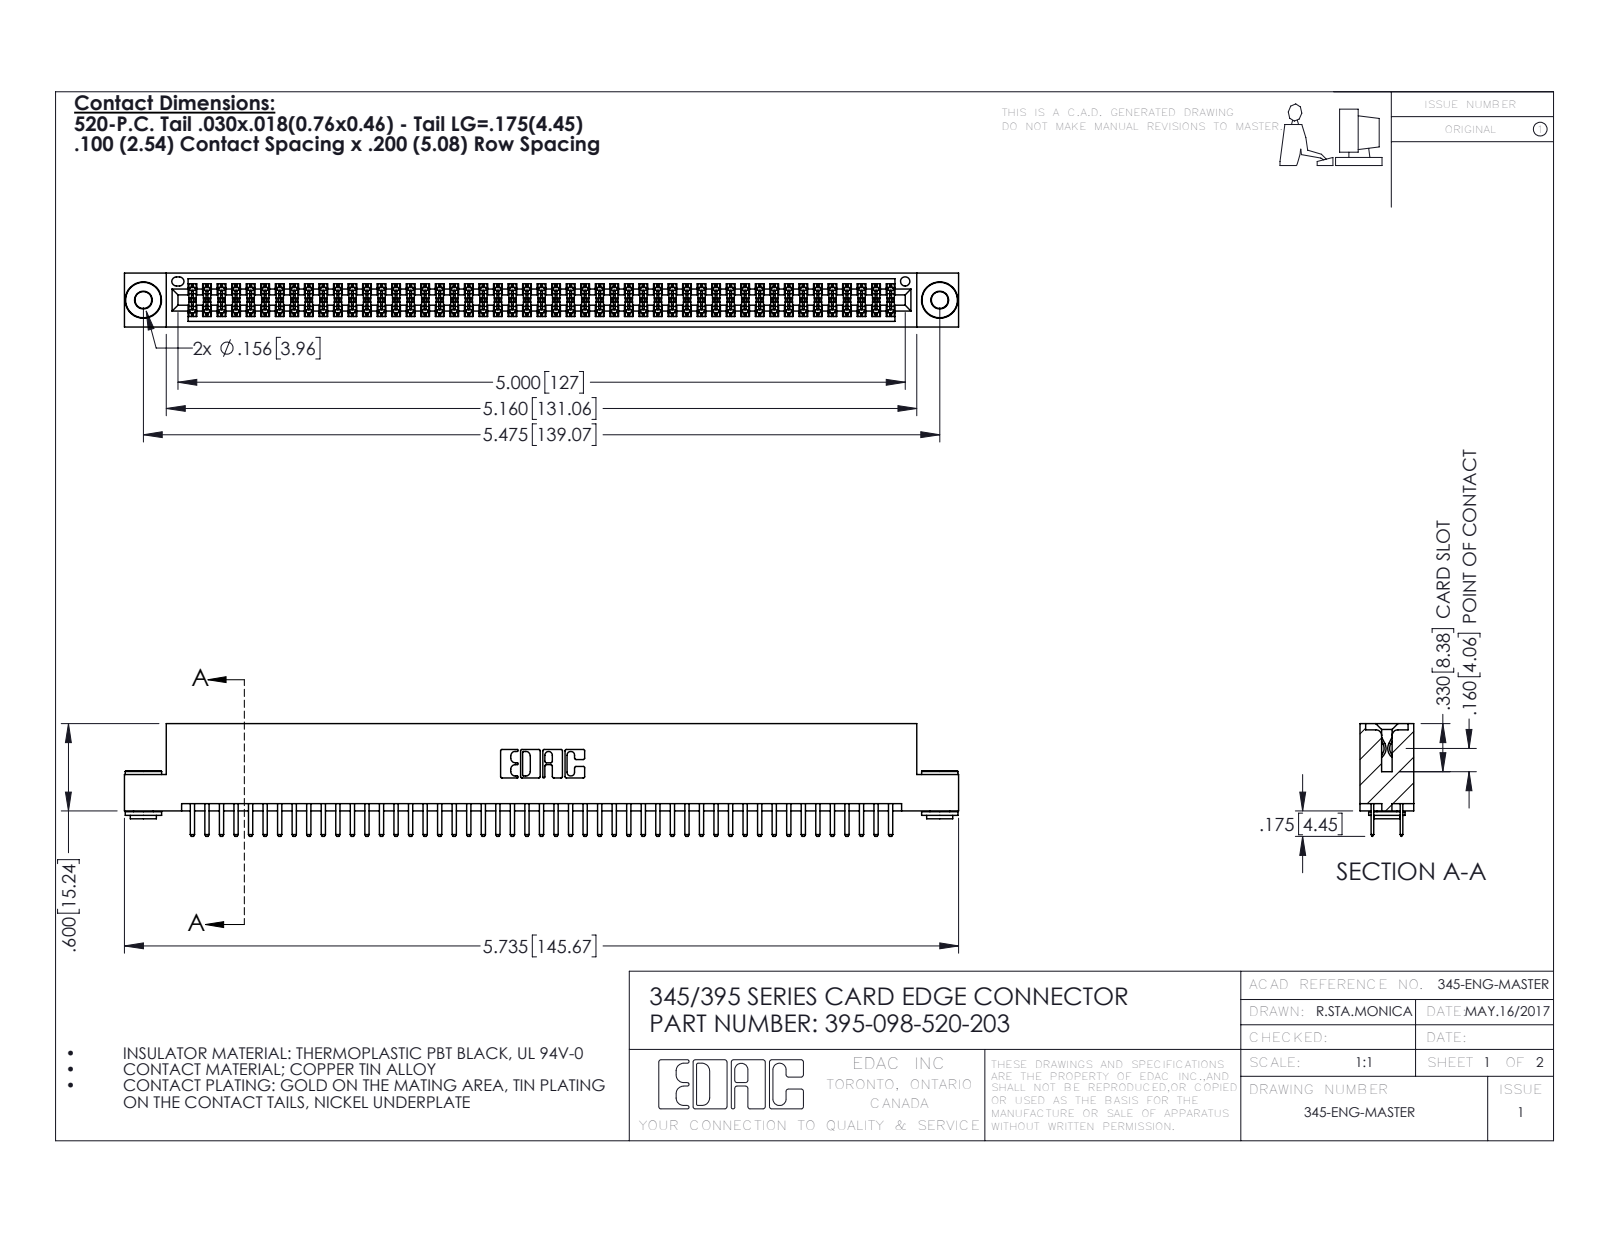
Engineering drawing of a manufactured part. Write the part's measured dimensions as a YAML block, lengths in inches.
part_name: "345 Part_Flush Mounting Lugs - 0.156 Dia-TH; 345-250-002_345-250-002-102; 395-098-520-203; 345-292-001_345-293-120"
step_written_by: "SolidWorks 2016 (CONFIG_CONTROL_DESIGN)"
units: inches
bodies: {solids: 101, faces: 5456, planar: 3520, cylindrical: 1928, other: 8}
overall_size: [5.735, 0.775, 0.37]
volume: 0.866
surface_area: 32.9
round_holes:
  - {diameter: 0.116, count: 2}
  - {diameter: 0.156, count: 2}
  - {diameter: 0.064, count: 1}
round_bosses_or_shafts:
  - {diameter: 0.25, count: 2}
  - {diameter: 0.18, count: 2}
  - {diameter: 0.136, count: 2}
partial_cylinders:
  - {radius: 0.006, count: 147}
  - {radius: 0.01, count: 102}
  - {radius: 0.01, count: 22}
  - {radius: 0.007, count: 6}
  - {radius: 0.031, count: 6}
  - {radius: 0.026, count: 3}
  - {radius: 0.014, count: 2}
  - {radius: 0.019, count: 2}
face_to_face_distances: [0.072, 0.298, 0.2, 0.37, 0.025, 0.098, 0.272, 0.225, 0.022, 0.072]
hole_center_spacings: [0.27, 5.239, 5.475]
